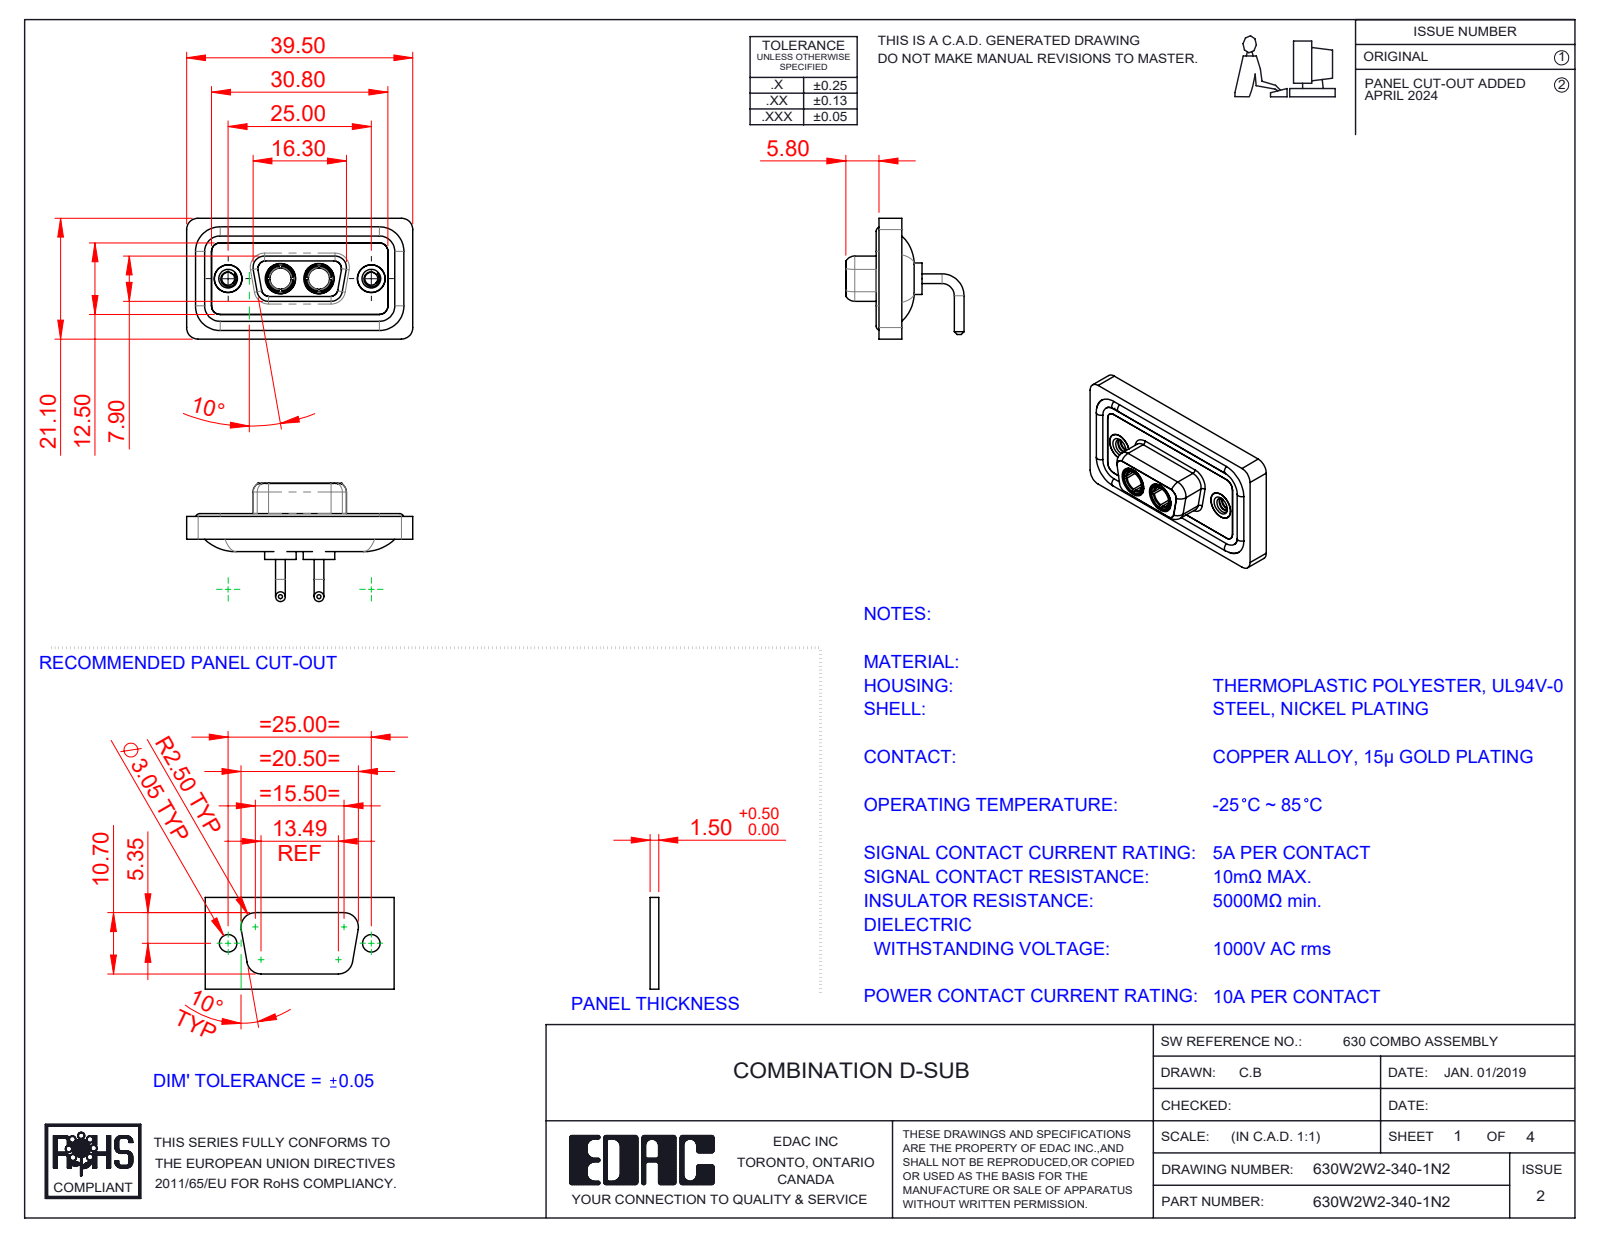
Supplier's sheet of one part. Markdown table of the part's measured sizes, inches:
| quantity | value |
| --- | --- |
| part name | 630Combo Threaded Rivet_2; 630Combo Shell Front_09 Contacts; Power Socket_10A RA; 630Combo Housing_2W2 (+3 more) |
| STEP written by | SolidWorks 2023 (CONFIG_CONTROL_DESIGN) |
| units | inches |
| bodies | 11 solids, 542 faces (163 planar, 238 cylindrical, 141 other) |
| overall size | 1.555 × 0.831 × 0.813 |
| volume | 0.287 in³ |
| surface area | 11.91 in² |
| round holes (diameter × count) | 0.191 × 4, 0.089 × 2, 0.146 × 2, 0.157 × 2, 0.159 × 2, 0.197 × 2, 0.209 × 2 |
| round bosses / shafts (diameter × count) | 0.067 × 4, 0.063 × 4, 0.217 × 2, 0.205 × 2, 0.195 × 2, 0.195 × 2, 0.189 × 2, 0.187 × 2 |
| partial cylindrical surfaces (radius × count) | 0.059 × 18, 0.079 × 18, 0.053 × 8, 0.063 × 8, 0.01 × 4, 0.02 × 4, 0.024 × 4, 0.026 × 4 |
| main face-to-face distances | 0.016, 0.071, 0.043, 0.114, 0.098, 0.063, 0.122, 0.059, 0.083, 0.02 |
| hole center spacings | 0.36, 0.624, 0.265, 0.984 |
